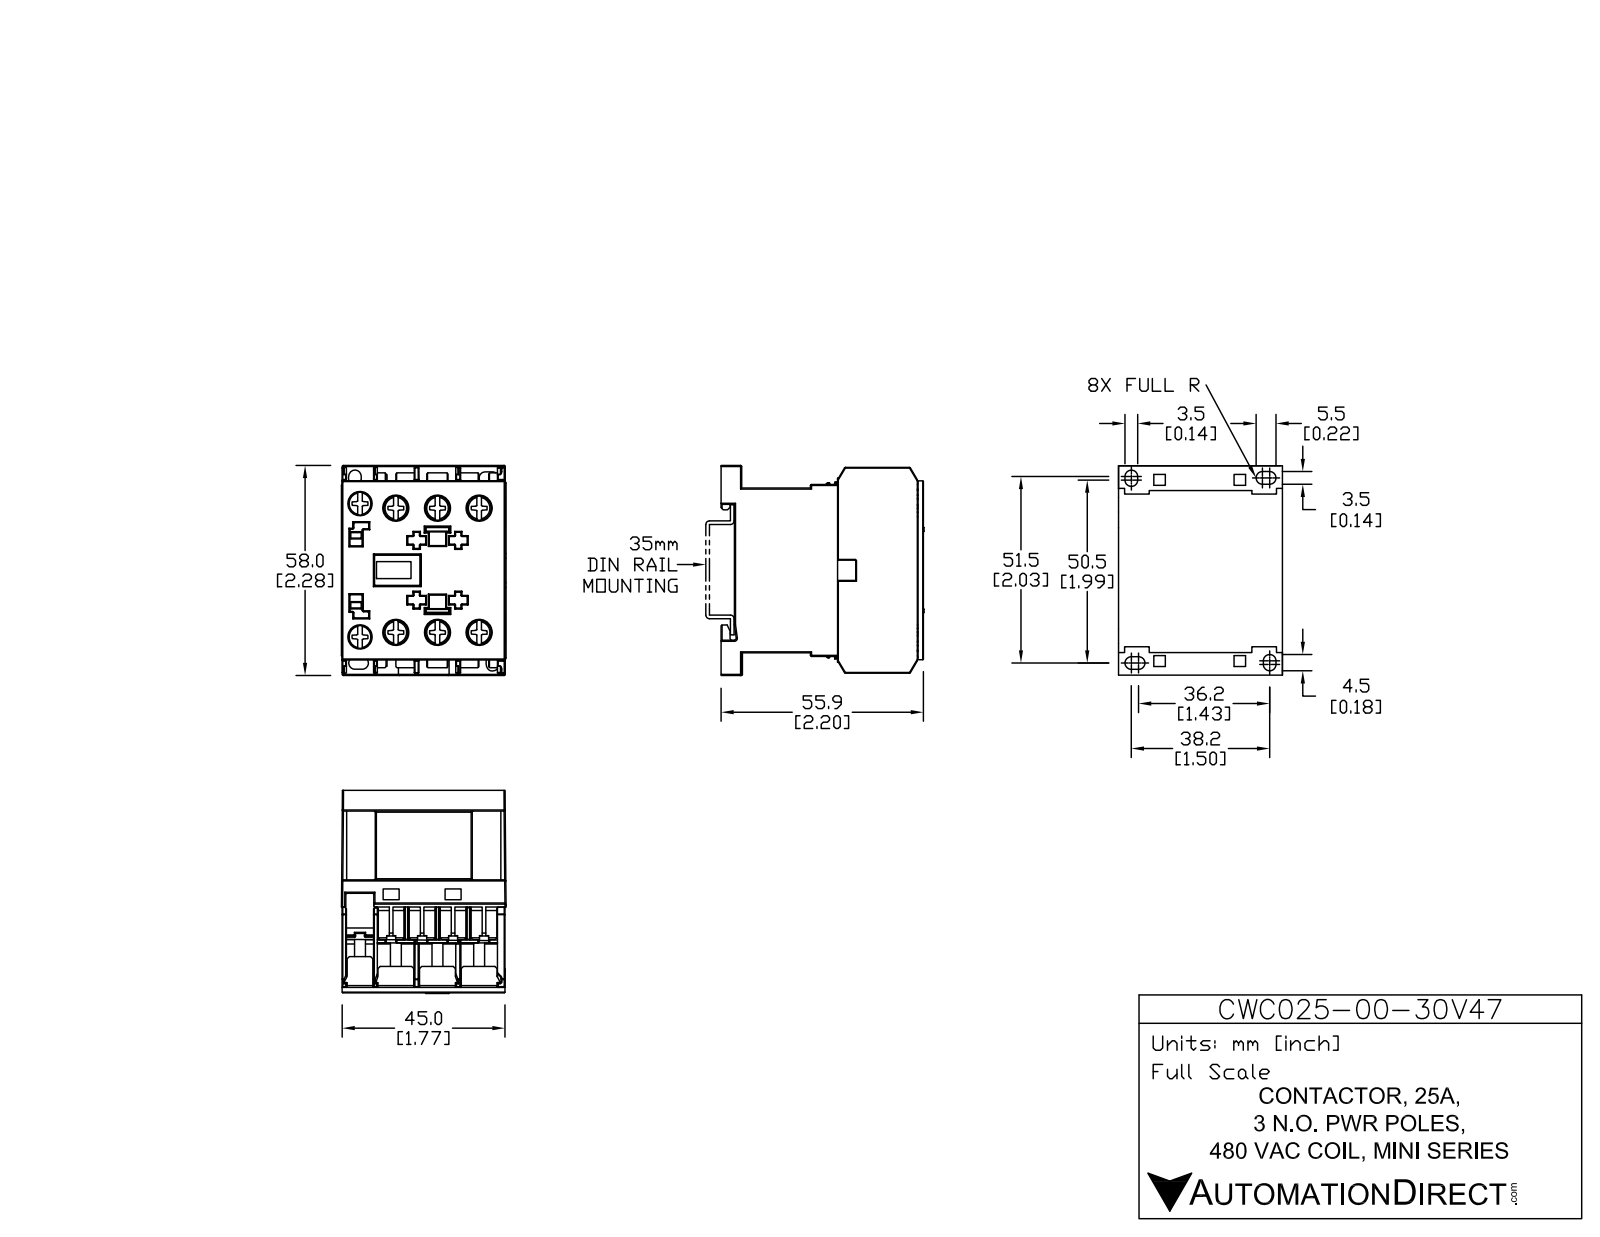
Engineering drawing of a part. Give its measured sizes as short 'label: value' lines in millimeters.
name: CWC025-00-30V47
written by: SolidWorks 2013 (AUTOMOTIVE_DESIGN)
unit: mm
bodies: 2 solids, 746 faces (639 planar, 107 cylindrical, 0 other)
size: 58 × 55.7 × 45
volume: 92 387 mm³; area: 34 434 mm²
holes: 6× ⌀6.85, 2× ⌀6.5
bosses: 6× ⌀6.5, 6× ⌀3.5, 2× ⌀5.25, 2× ⌀2.75
rounds: 14× R0.2, 10× R0.5, 8× R1.72, 7× R0.3
face distances: 45, 1, 23.5, 28.5, 28.53, 52, 23.47, 37.35, 8.85, 8.82
hole spacings: 11.5, 36.37, 34.5, 9.55, 21.02, 23, 32.52, 36.75
